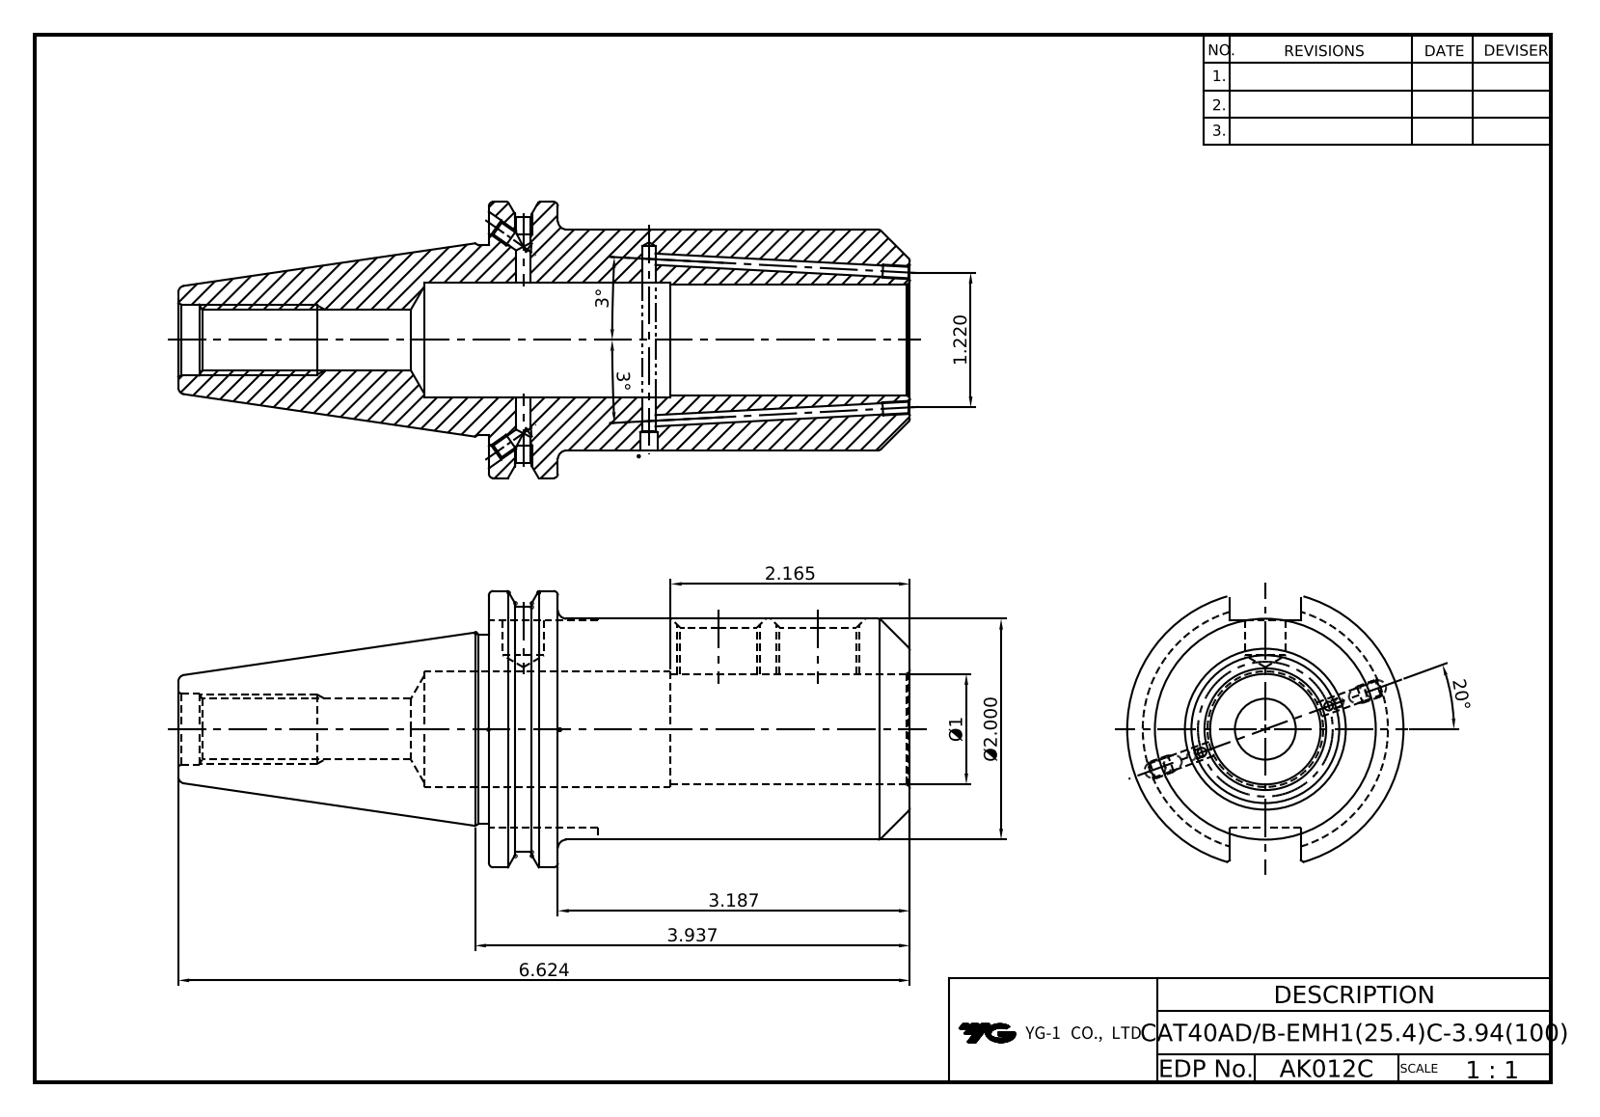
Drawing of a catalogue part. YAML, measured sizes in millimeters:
part_name: "CAT40ADB-EMH25_4C-100-PB15"
step_written_by: "CREO PARAMETRIC BY PTC INC, 2018400 (CONFIG_CONTROL_DESIGN)"
units: millimeters
bodies: {solids: 1, faces: 169, planar: 49, cylindrical: 80, other: 40}
overall_size: [168.25, 63.5, 60.84]
volume: 192728
surface_area: 46986
round_holes:
  - {diameter: 4, count: 4}
  - {diameter: 3, count: 3}
  - {diameter: 3.3, count: 3}
  - {diameter: 2.5, count: 2}
  - {diameter: 17.7, count: 2}
  - {diameter: 19.05, count: 2}
  - {diameter: 4.2, count: 1}
  - {diameter: 9.53, count: 1}
  - {diameter: 13.49, count: 1}
  - {diameter: 15.88, count: 1}
  - {diameter: 16.3, count: 1}
  - {diameter: 25.4, count: 1}
round_bosses_or_shafts:
  - {diameter: 63.5, count: 1}
  - {diameter: 50.8, count: 1}
  - {diameter: 43.6, count: 1}
partial_cylinders:
  - {radius: 8.19, count: 2}
  - {radius: 28.15, count: 1}
face_to_face_distances: [15.88, 96.83, 80.95, 23.2, 39.08, 120.03, 47.6, 16.38, 48.22, 71.42]
hole_center_spacings: [28.87, 22.9, 44.9, 67.8]
